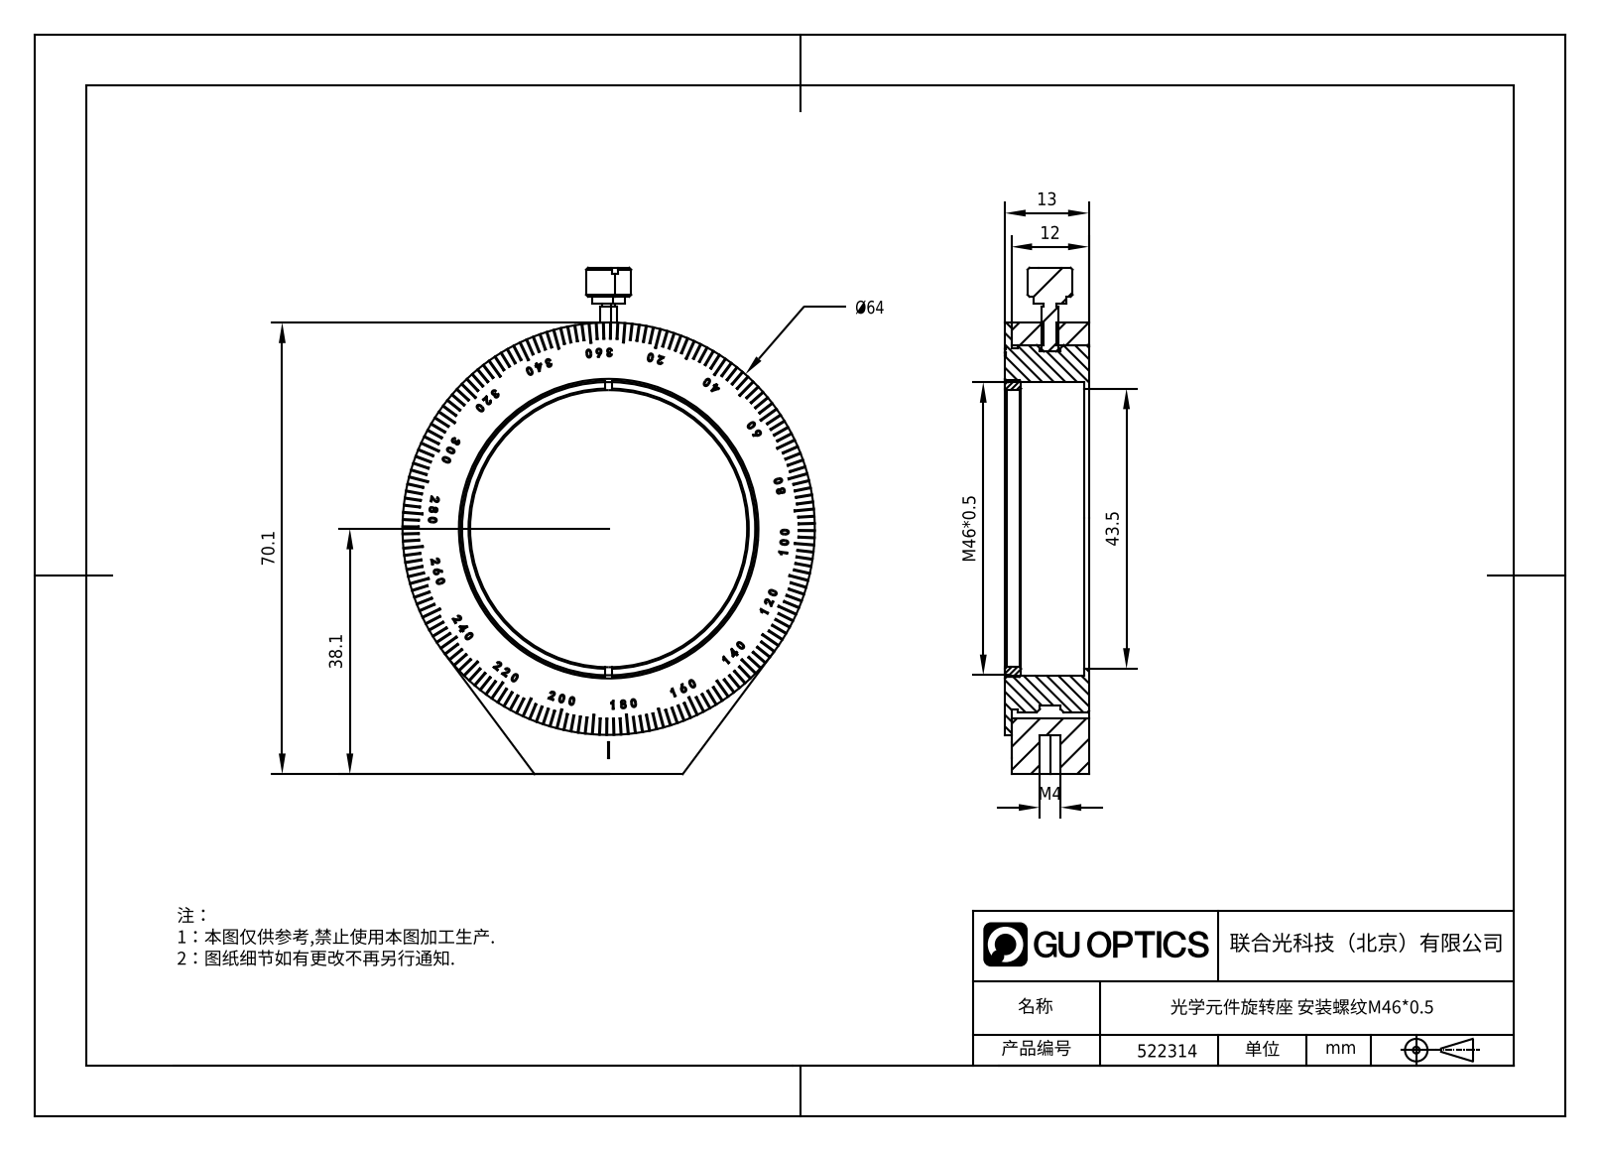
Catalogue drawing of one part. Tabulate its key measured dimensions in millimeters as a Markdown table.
| quantity | value |
| --- | --- |
| part name | ZFK透镜卡环压圈_1.8.5.17-ZFK-K45; 一体式手拧螺丝_30.13.2.2.5-SNTY-M2.5x7.5-0713 |
| STEP written by | SolidWorks 2021 (CONFIG_CONTROL_DESIGN) |
| units | millimeters |
| bodies | 4 solids, 1222 faces (991 planar, 35 cylindrical, 196 other) |
| overall size | 78.6 × 64 × 13.05 |
| volume | 23 417 mm³ |
| surface area | 15 979 mm² |
| round holes (diameter × count) | 2.05 × 1, 3.3 × 1, 43 × 1, 43.5 × 1, 45.5 × 1 |
| round bosses / shafts (diameter × count) | 64 × 1, 57 × 1, 56 × 1, 55 × 1, 46 × 1, 7 × 1, 5 × 1, 2.5 × 1 |
| partial cylindrical surfaces (radius × count) | 24.5 × 1 |
| main face-to-face distances | 1, 12.05, 13.05, 12, 13, 0.8, 1.5, 2.5, 0.75, 11.25 |
